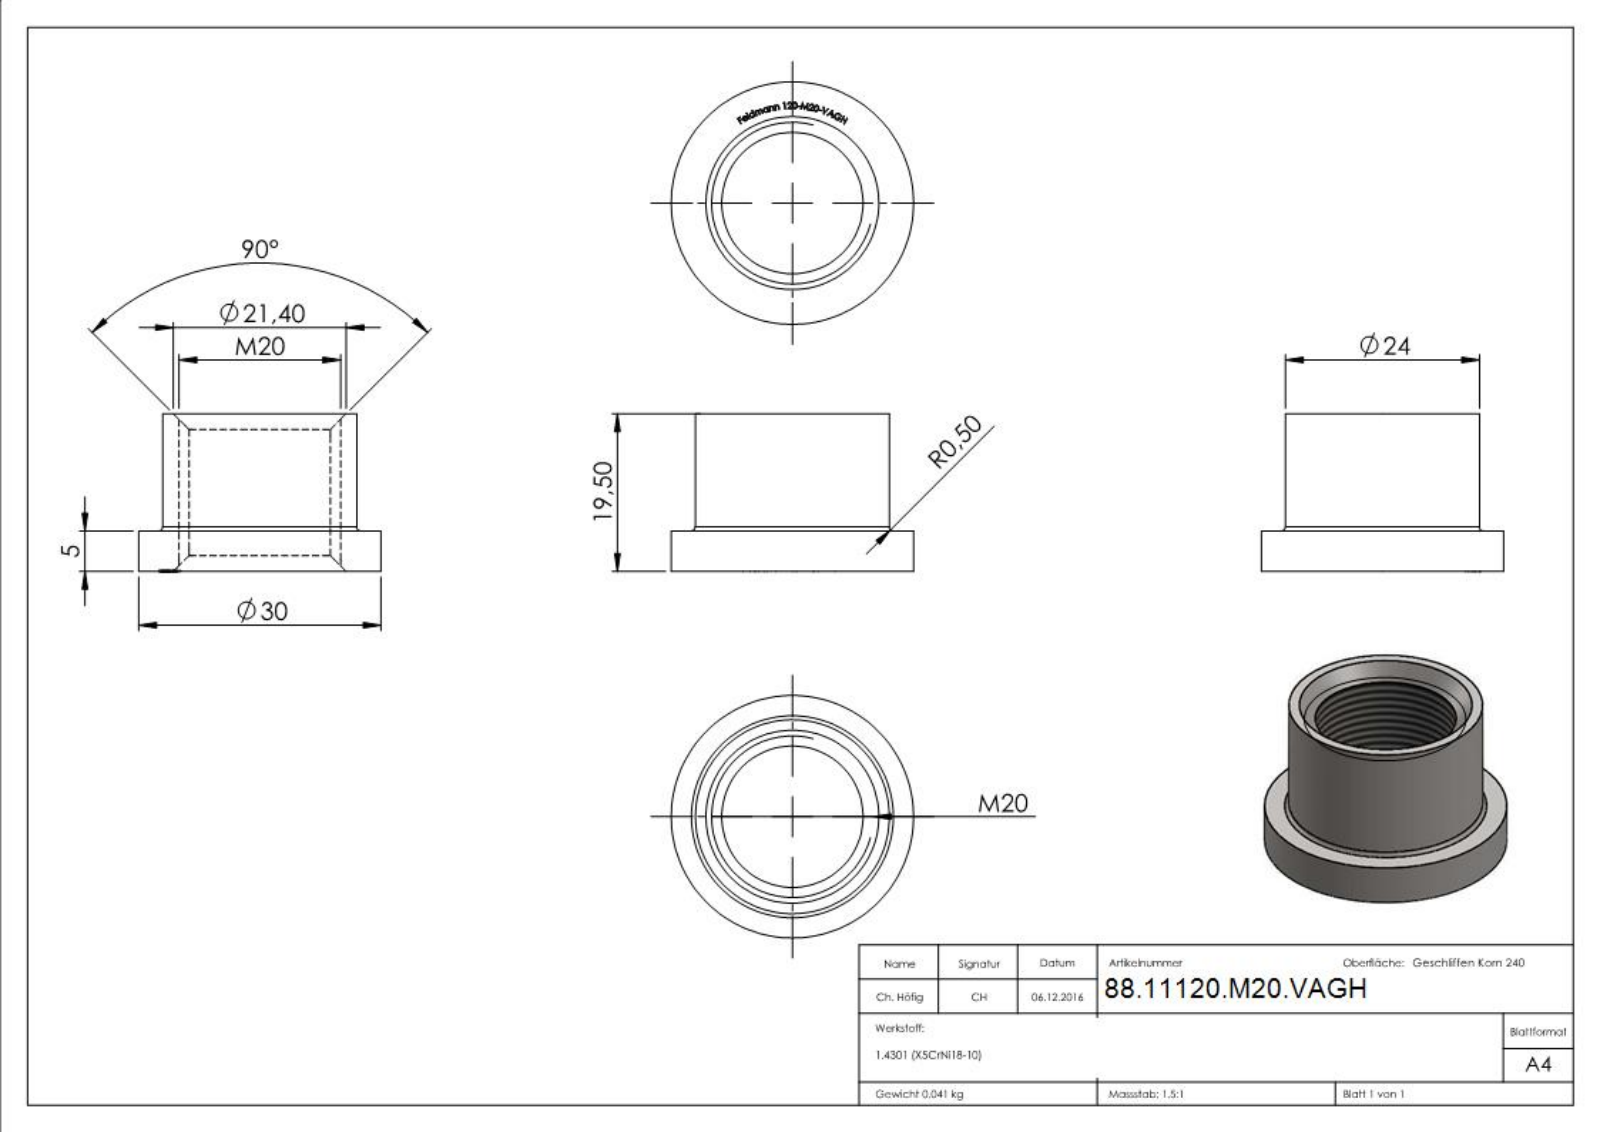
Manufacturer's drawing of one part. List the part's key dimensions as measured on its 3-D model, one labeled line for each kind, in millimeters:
Part name (STEP PRODUCT): 120-M20-VAGH
STEP written by: SolidWorks 2015 (CONFIG_CONTROL_DESIGN)
Units: millimetres
Bodies: 1 solid, 255 faces (156 planar, 6 cylindrical, 93 other)
Overall size (bounding box): 30 × 30 × 19.5
Volume: 5 183 mm³ · Surface area: 3 444 mm²
Round holes (diameter × count): ⌀17.5 ×1
Round bosses / shafts (diameter × count): ⌀30 ×1, ⌀24 ×1
Main face-to-face distances: 5, 19.5, 14.5, 4.9, 19.4, 0.49, 0.43, 0.57, 0.41, 0.32
